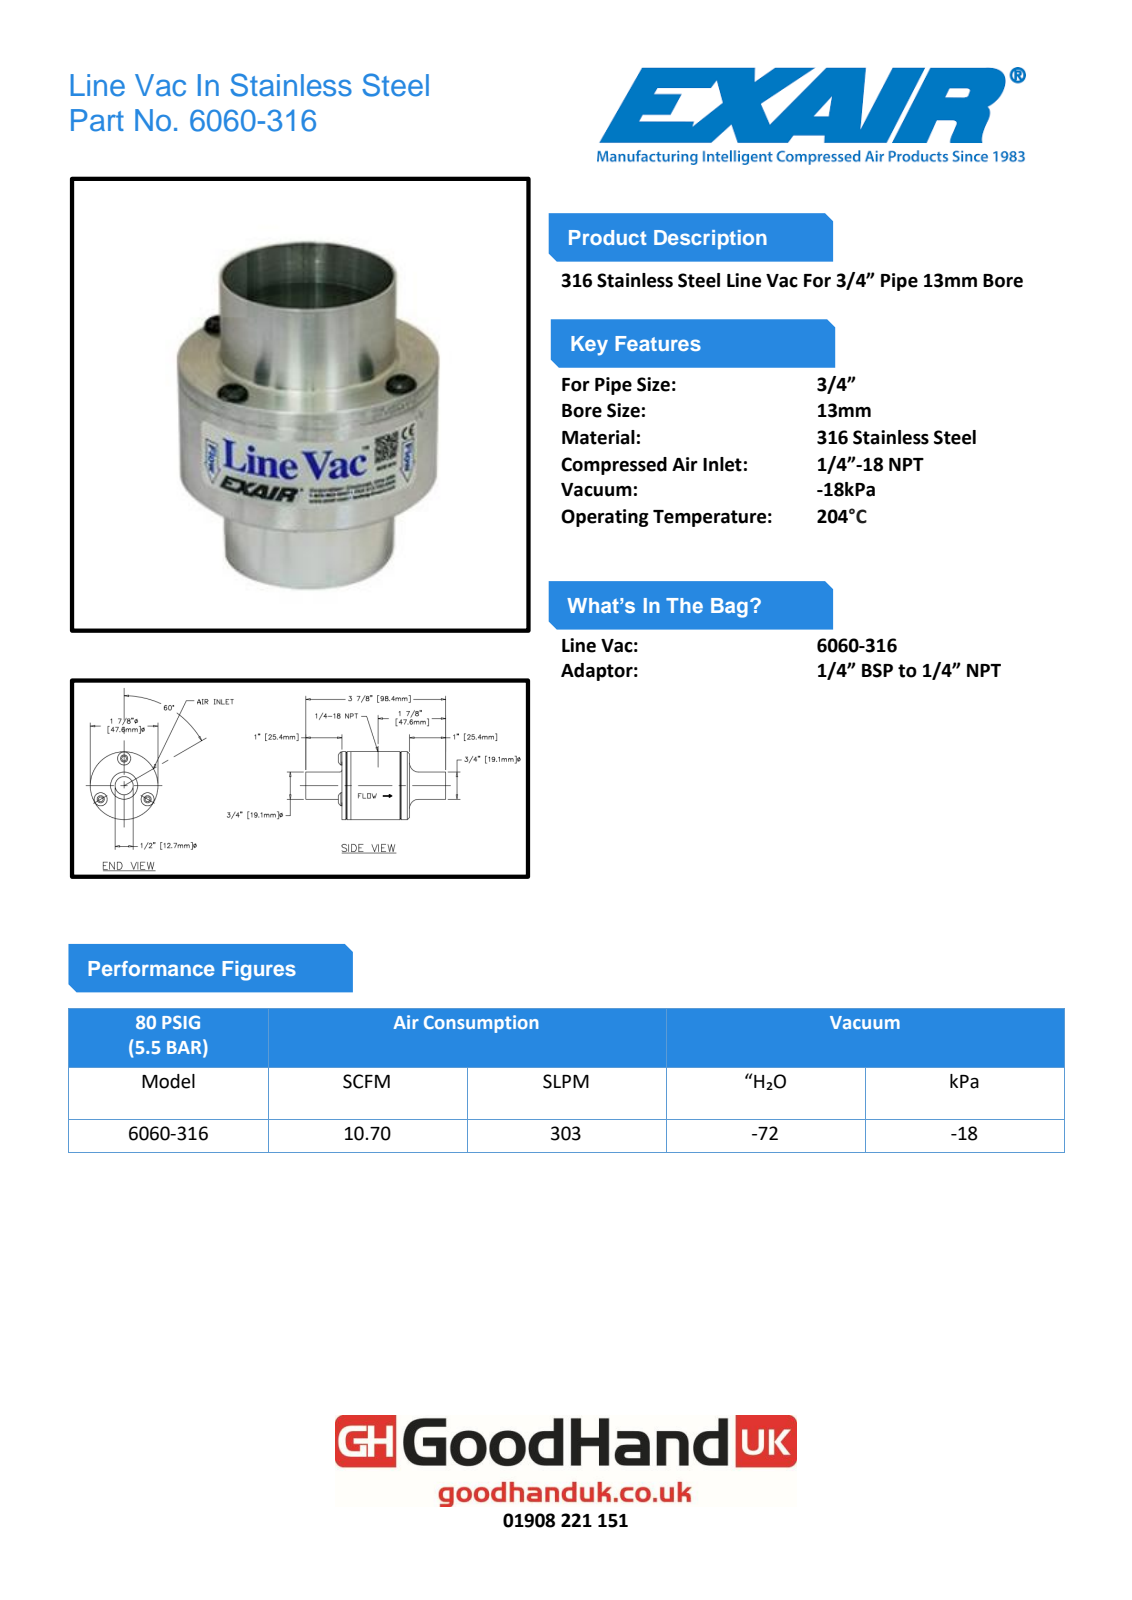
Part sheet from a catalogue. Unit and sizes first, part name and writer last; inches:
Units: inches
Overall size (bounding box): 3.875 × 1.875 × 1.875
Round holes (diameter × count): ⌀0.152 ×3, ⌀0.186 ×3, ⌀0.218 ×3, ⌀0.438 ×1, ⌀0.5 ×1, ⌀1.15 ×1
Round bosses / shafts (diameter × count): ⌀0.361 ×3, ⌀0.19 ×3, ⌀1.875 ×1, ⌀0.75 ×1
Main face-to-face distances: 0.25, 0.125, 0.375, 1.875, 1.625, 1.5, 0.252, 0.377, 1.877, 1
Hole centre spacings: 0.75, 1.298
Volume: 5.113 in³ · Surface area: 36.8 in²
Bodies: 5 solids, 84 faces (42 planar, 24 cylindrical, 18 other)
STEP written by: Autodesk Inventor 2010 (AUTOMOTIVE_DESIGN)
